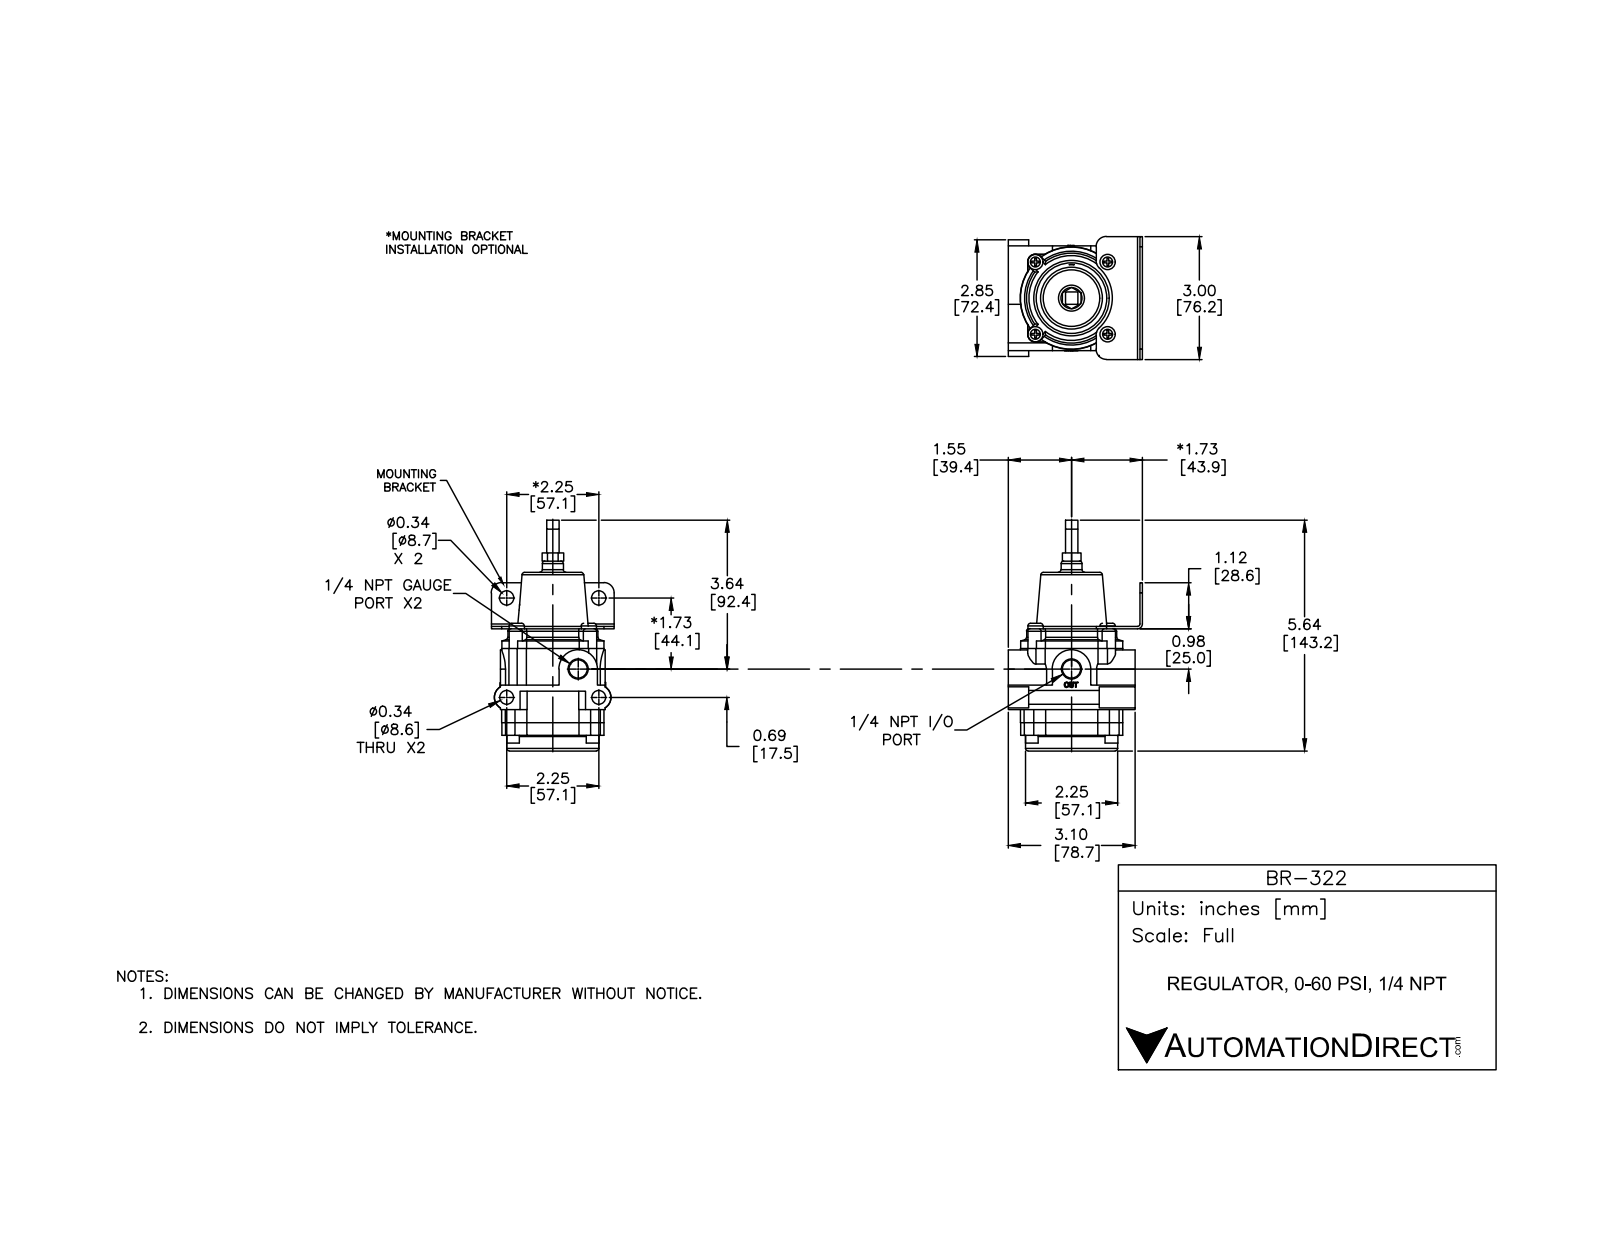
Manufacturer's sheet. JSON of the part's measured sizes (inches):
{"part_name": "BR-322", "step_written_by": "SolidWorks 2015 (CONFIG_CONTROL_DESIGN)", "units": "inches", "bodies": {"solids": 13, "faces": 1460, "planar": 268, "cylindrical": 963, "other": 229}, "overall_size": [5.613, 3.1, 2.85], "volume_in3": 18.6, "surface_area_in2": 96.84, "round_holes": [[0.159, 8], [0.201, 8], [0.34, 2], [0.438, 2], [0.257, 1]], "round_bosses_or_shafts": [[0.19, 8], [0.149, 8], [0.312, 5], [0.373, 4], [2.2, 1], [0.512, 1], [0.203, 1]], "partial_cylinders_radius": [[0.004, 48], [0.187, 8], [0.188, 8], [0.02, 6], [0.062, 4], [0.063, 3], [0.3, 2], [0.469, 2]], "face_to_face_distances": [1.81, 0.695, 2.505, 1.61, 0.915, 0.895, 0.385, 0.31, 1.225, 2.12], "hole_center_spacings": [1.858, 0.125, 1.944, 1.375, 1.25, 1.25, 1.768, 1.768]}
